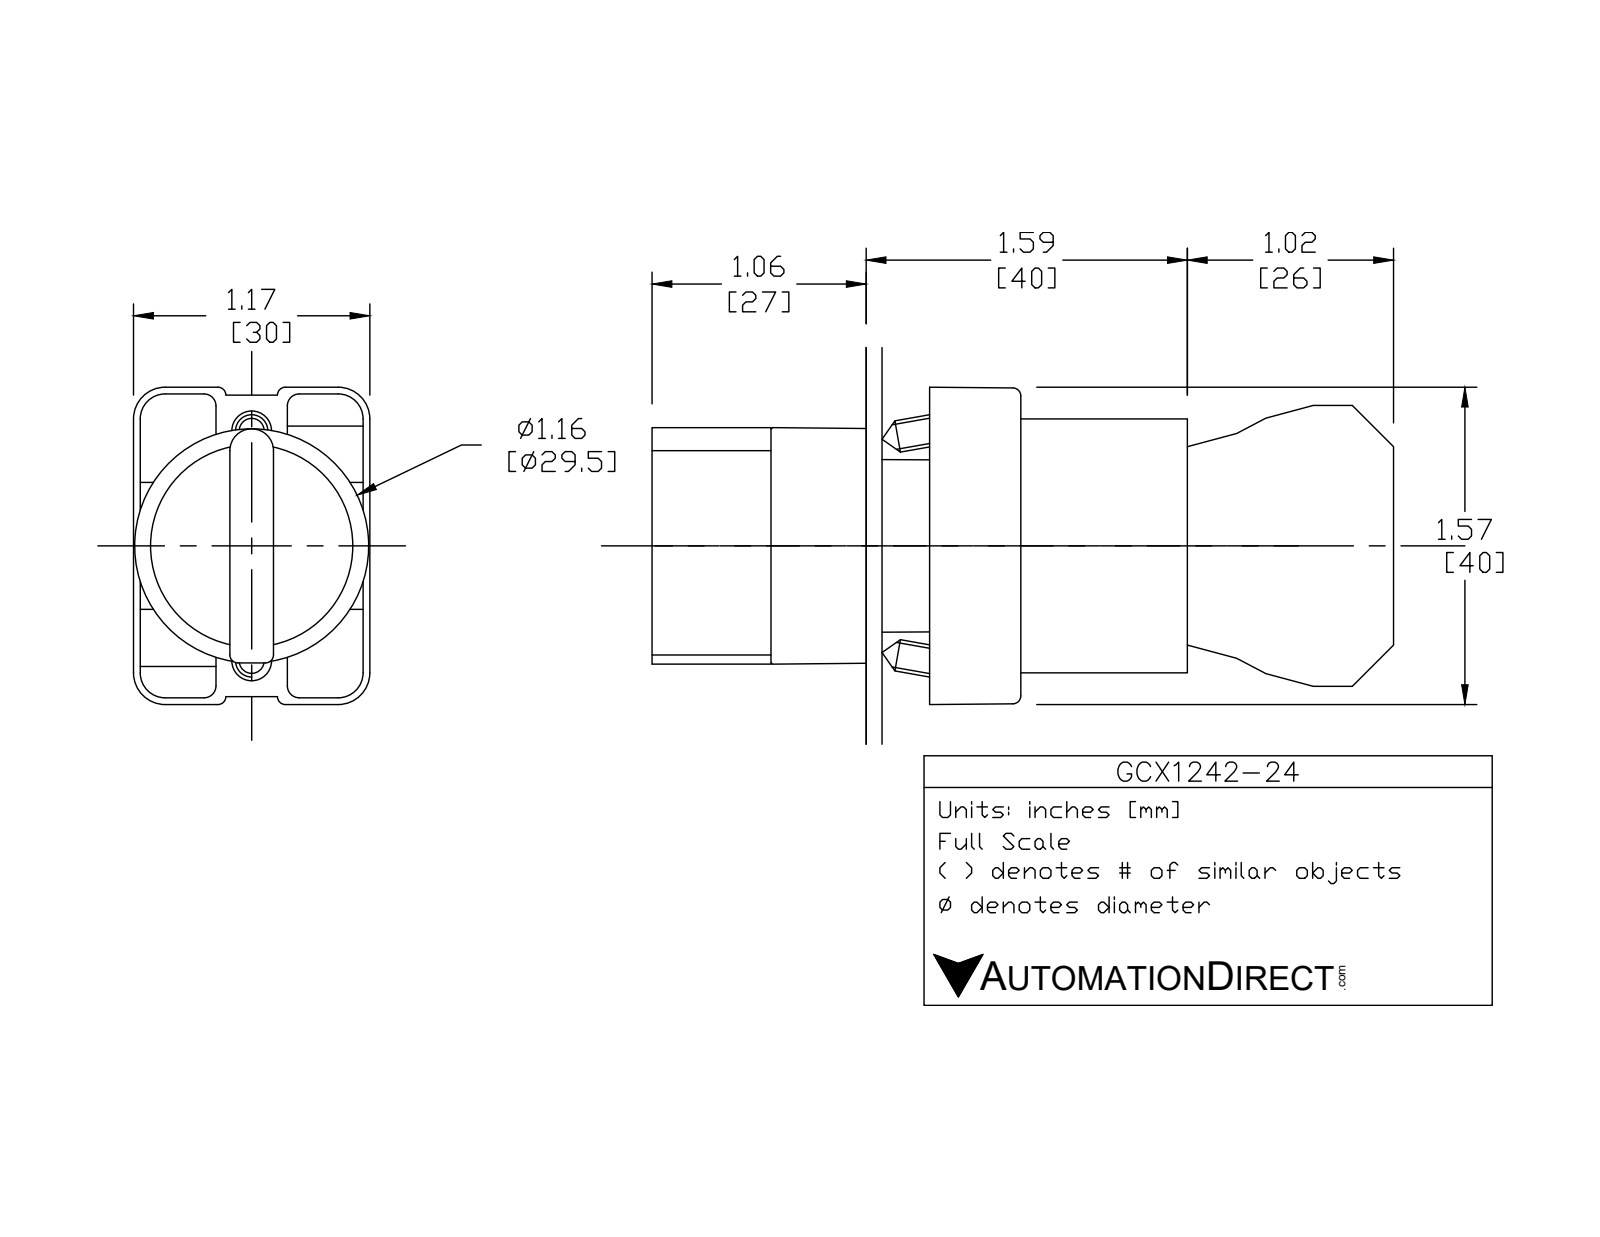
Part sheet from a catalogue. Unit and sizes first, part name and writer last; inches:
Units: inches
Overall size (bounding box): 3.653 × 1.581 × 1.177
Round holes (diameter × count): ⌀0.079 ×2, ⌀0.124 ×2, ⌀0.13 ×2, ⌀0.087 ×1, ⌀0.197 ×1, ⌀0.469 ×1, ⌀0.878 ×1, ⌀0.888 ×1, ⌀1.024 ×1
Round bosses / shafts (diameter × count): ⌀0.157 ×4, ⌀1.175 ×1, ⌀1.004 ×1, ⌀0.945 ×1, ⌀0.856 ×1, ⌀0.78 ×1, ⌀0.504 ×1
Partial cylindrical surfaces — rounded edges, fillets, slot ends (radius × count): R0.059 ×24, R0.041 ×12, R0.124 ×12, R0.157 ×12, R0.039 ×9, R0.128 ×2, R0.02 ×1, R0.063 ×1
Main face-to-face distances: 0.827, 2.02, 1.193, 0.579, 1.244, 1.171, 0.472, 0.469, 0.031, 0.033
Hole centre spacings: 0.236, 0.544, 0.472, 0.49
Volume: 2.799 in³ · Surface area: 39 in²
Bodies: 8 solids, 445 faces (263 planar, 151 cylindrical, 31 other)
Part name (STEP PRODUCT): GCX1242 OPERATOR; ecx1040; ECX1050; ecx1029 (+1 more)
STEP written by: SolidWorks 2016 (AUTOMOTIVE_DESIGN)
